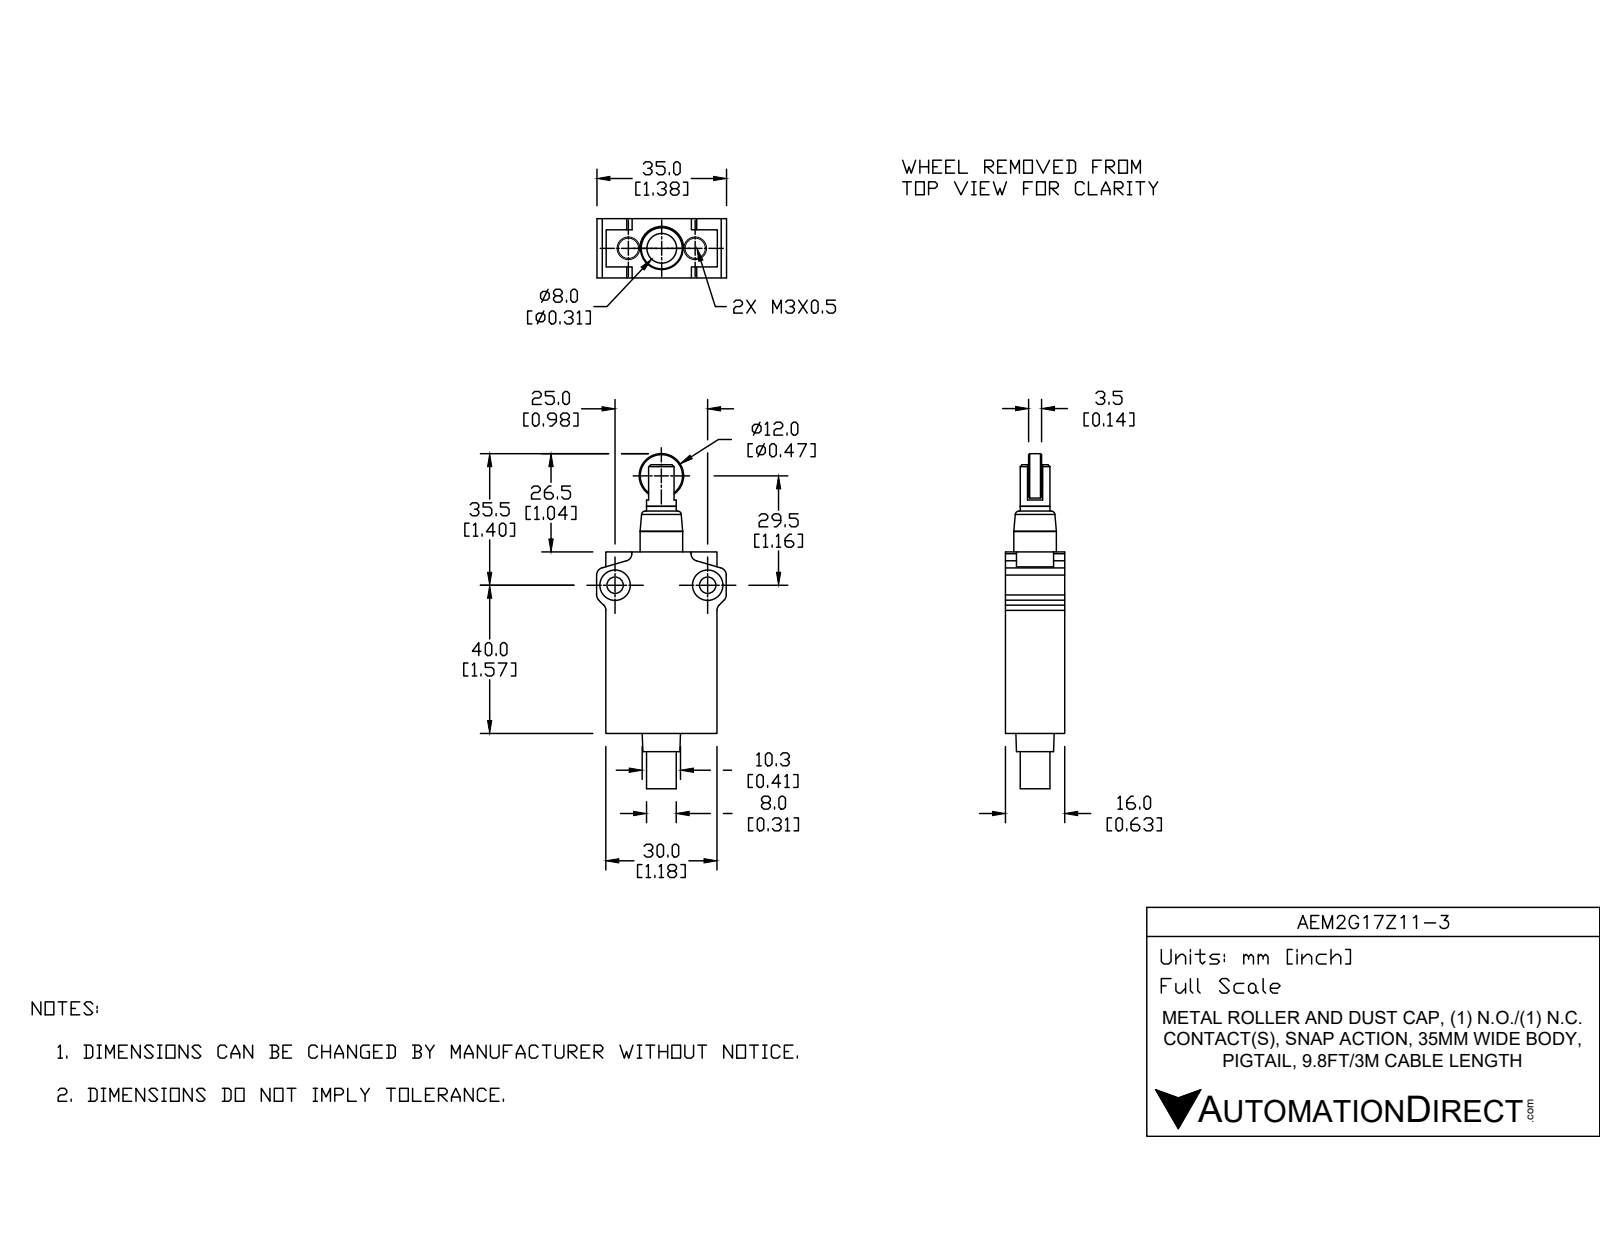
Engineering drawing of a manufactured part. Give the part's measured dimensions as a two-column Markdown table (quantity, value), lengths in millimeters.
| quantity | value |
| --- | --- |
| part name | AEM2G17Z11-3 |
| STEP written by | SolidWorks 2017 (AUTOMOTIVE_DESIGN) |
| units | millimeters |
| bodies | 5 solids, 131 faces (56 planar, 54 cylindrical, 21 other) |
| overall size | 91.4 × 35 × 16 |
| volume | 26 140 mm³ |
| surface area | 8 890 mm² |
| round holes (diameter × count) | 3 × 2, 4.4 × 2, 8.2 × 2 |
| round bosses / shafts (diameter × count) | 12 × 1, 11.5 × 1, 8 × 1, 6 × 1, 5.6 × 1 |
| partial cylindrical surfaces (radius × count) | 2 × 8, 6.5 × 1 |
| main face-to-face distances | 16, 30, 49, 12, 1, 3.8, 4, 6, 5.9, 4.8 |
| hole center spacings | 19, 25 |
